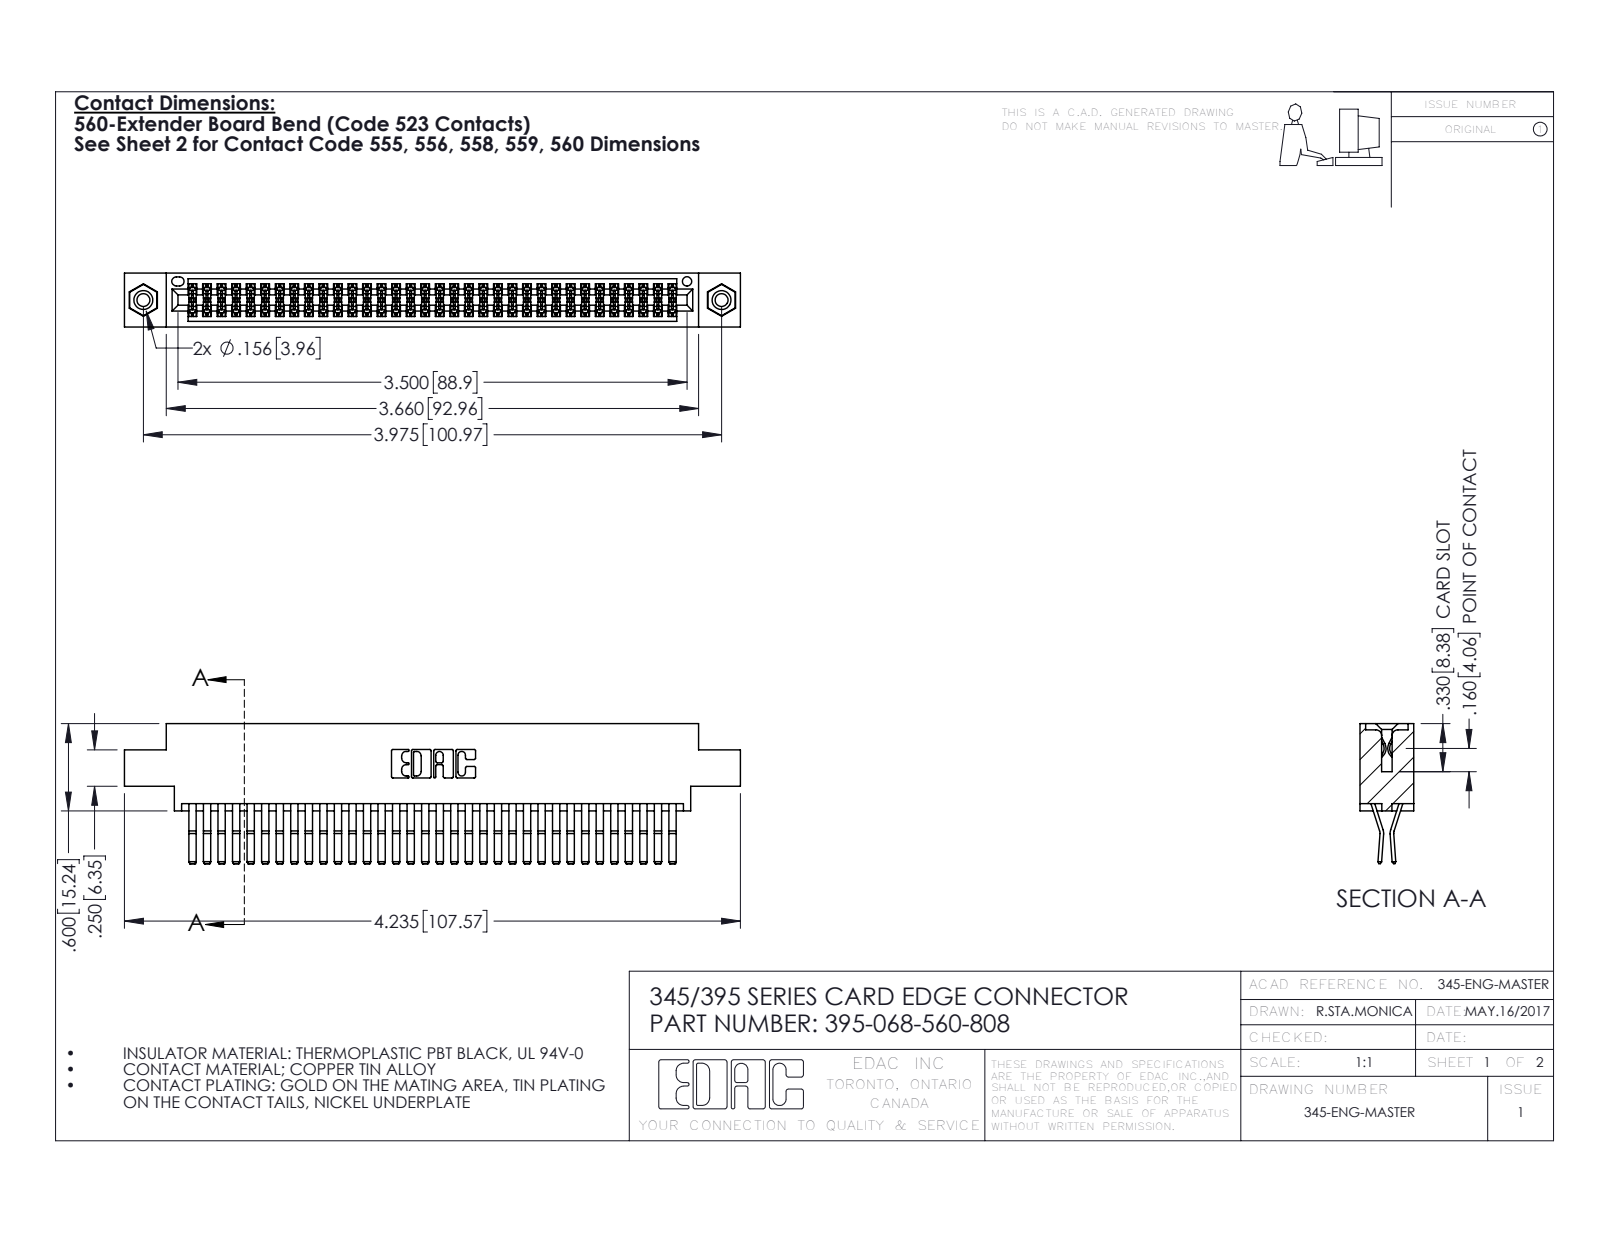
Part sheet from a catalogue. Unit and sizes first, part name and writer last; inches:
Units: inches
Overall size (bounding box): 4.235 × 0.962 × 0.37
Round holes (diameter × count): ⌀0.089 ×2, ⌀0.125 ×2, ⌀0.156 ×2, ⌀0.064 ×1
Round bosses / shafts (diameter × count): ⌀0.155 ×2
Partial cylindrical surfaces — rounded edges, fillets, slot ends (radius × count): R0.006 ×102, R0.01 ×22, R0.007 ×6, R0.031 ×6, R0.026 ×3, R0.01 ×2, R0.014 ×2, R0.019 ×2
Main face-to-face distances: 0.025, 0.072, 0.298, 0.37, 0.2, 0.098, 0.272, 0.225, 0.175, 0.149
Hole centre spacings: 0.27, 3.74, 3.975
Volume: 0.653 in³ · Surface area: 26.3 in²
Bodies: 71 solids, 3726 faces (2360 planar, 1350 cylindrical, 16 other)
Part name (STEP PRODUCT): 345 Part_0.170 Offset - 0.156 Dia-TI; 345-250-001_345-250-003-102; 395-068-560-808; 345-292-001_560 Tail
STEP written by: SolidWorks 2016 (CONFIG_CONTROL_DESIGN)
